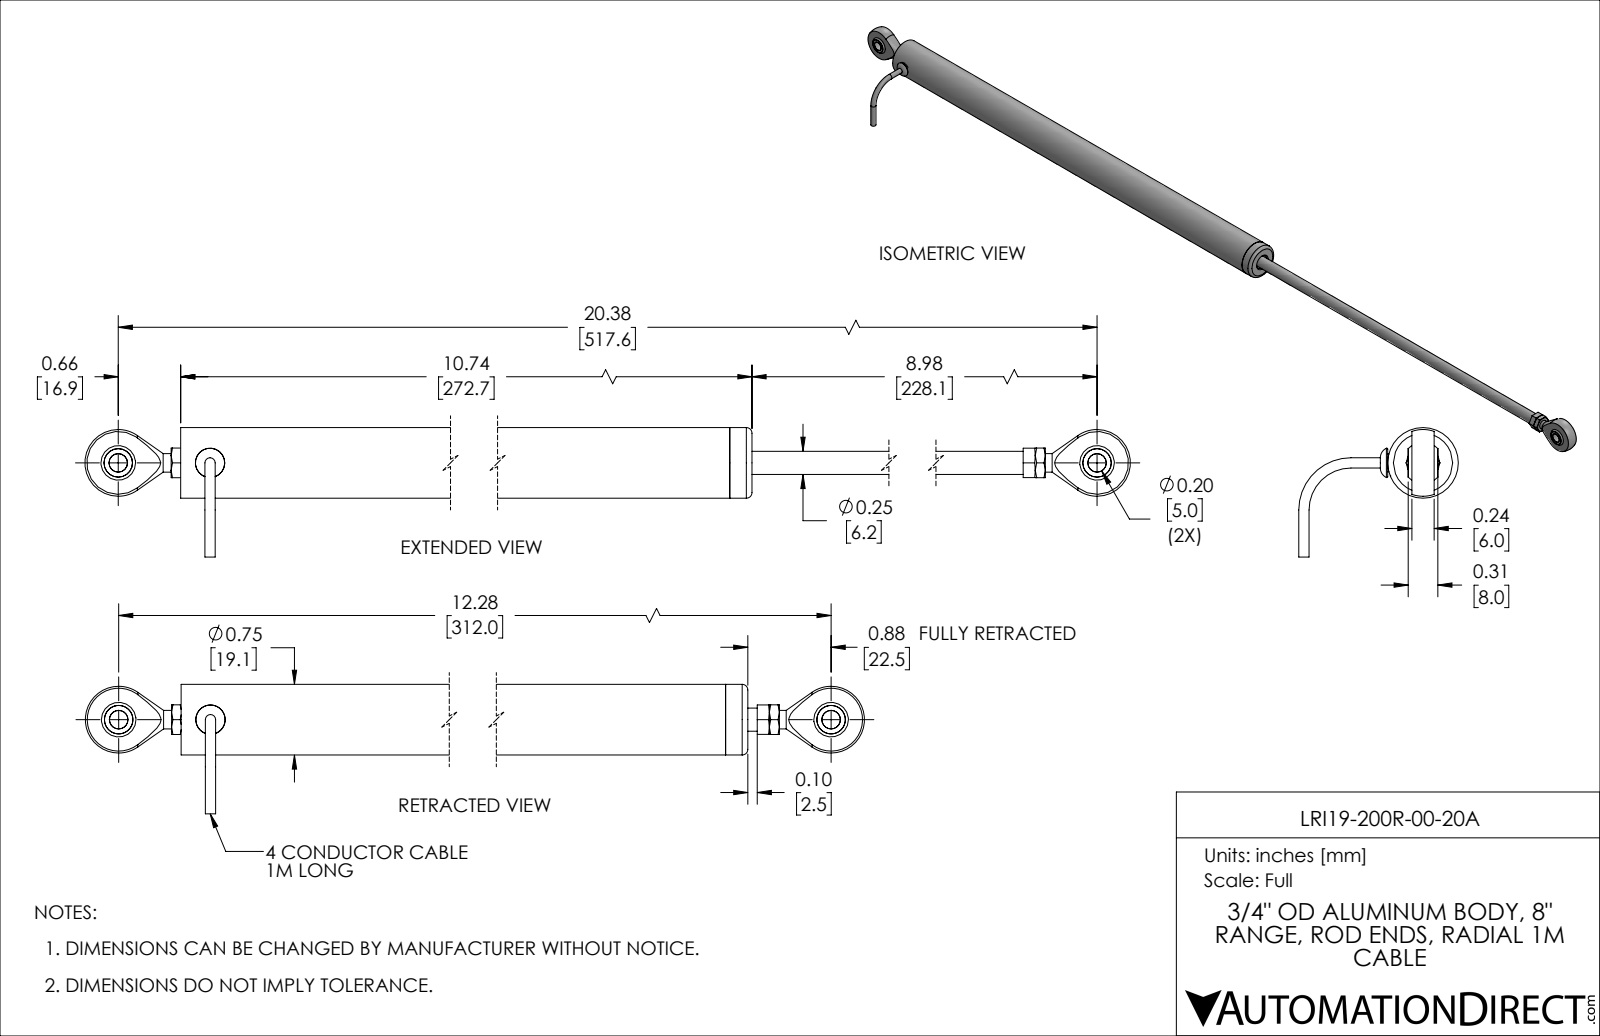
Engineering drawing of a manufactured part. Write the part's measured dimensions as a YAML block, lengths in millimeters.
part_name: "LRI19-200R-00-20A"
step_written_by: "SolidWorks 2019 (AUTOMOTIVE_DESIGN)"
units: millimeters
bodies: {solids: 13, faces: 157, planar: 58, cylindrical: 34, other: 65}
overall_size: [330, 43.1, 34.9]
volume: 33280
surface_area: 44720
round_holes:
  - {diameter: 5, count: 3}
  - {diameter: 2.8, count: 1}
  - {diameter: 4.2, count: 1}
  - {diameter: 4.8, count: 1}
  - {diameter: 4.9, count: 1}
  - {diameter: 5.6, count: 1}
  - {diameter: 7.8, count: 1}
  - {diameter: 15.7, count: 1}
  - {diameter: 15.9, count: 1}
  - {diameter: 16.5, count: 1}
  - {diameter: 18, count: 1}
  - {diameter: 18.4, count: 1}
round_bosses_or_shafts:
  - {diameter: 19.1, count: 1}
  - {diameter: 17.8, count: 1}
  - {diameter: 15.8, count: 1}
  - {diameter: 6.2, count: 1}
  - {diameter: 5.7, count: 1}
  - {diameter: 5.5, count: 1}
  - {diameter: 2.8, count: 1}
face_to_face_distances: [6, 2.7, 269.9, 272.6, 266.6, 263.9, 6, 8, 1, 7]
hole_center_spacings: [24.8, 287.2, 312]
